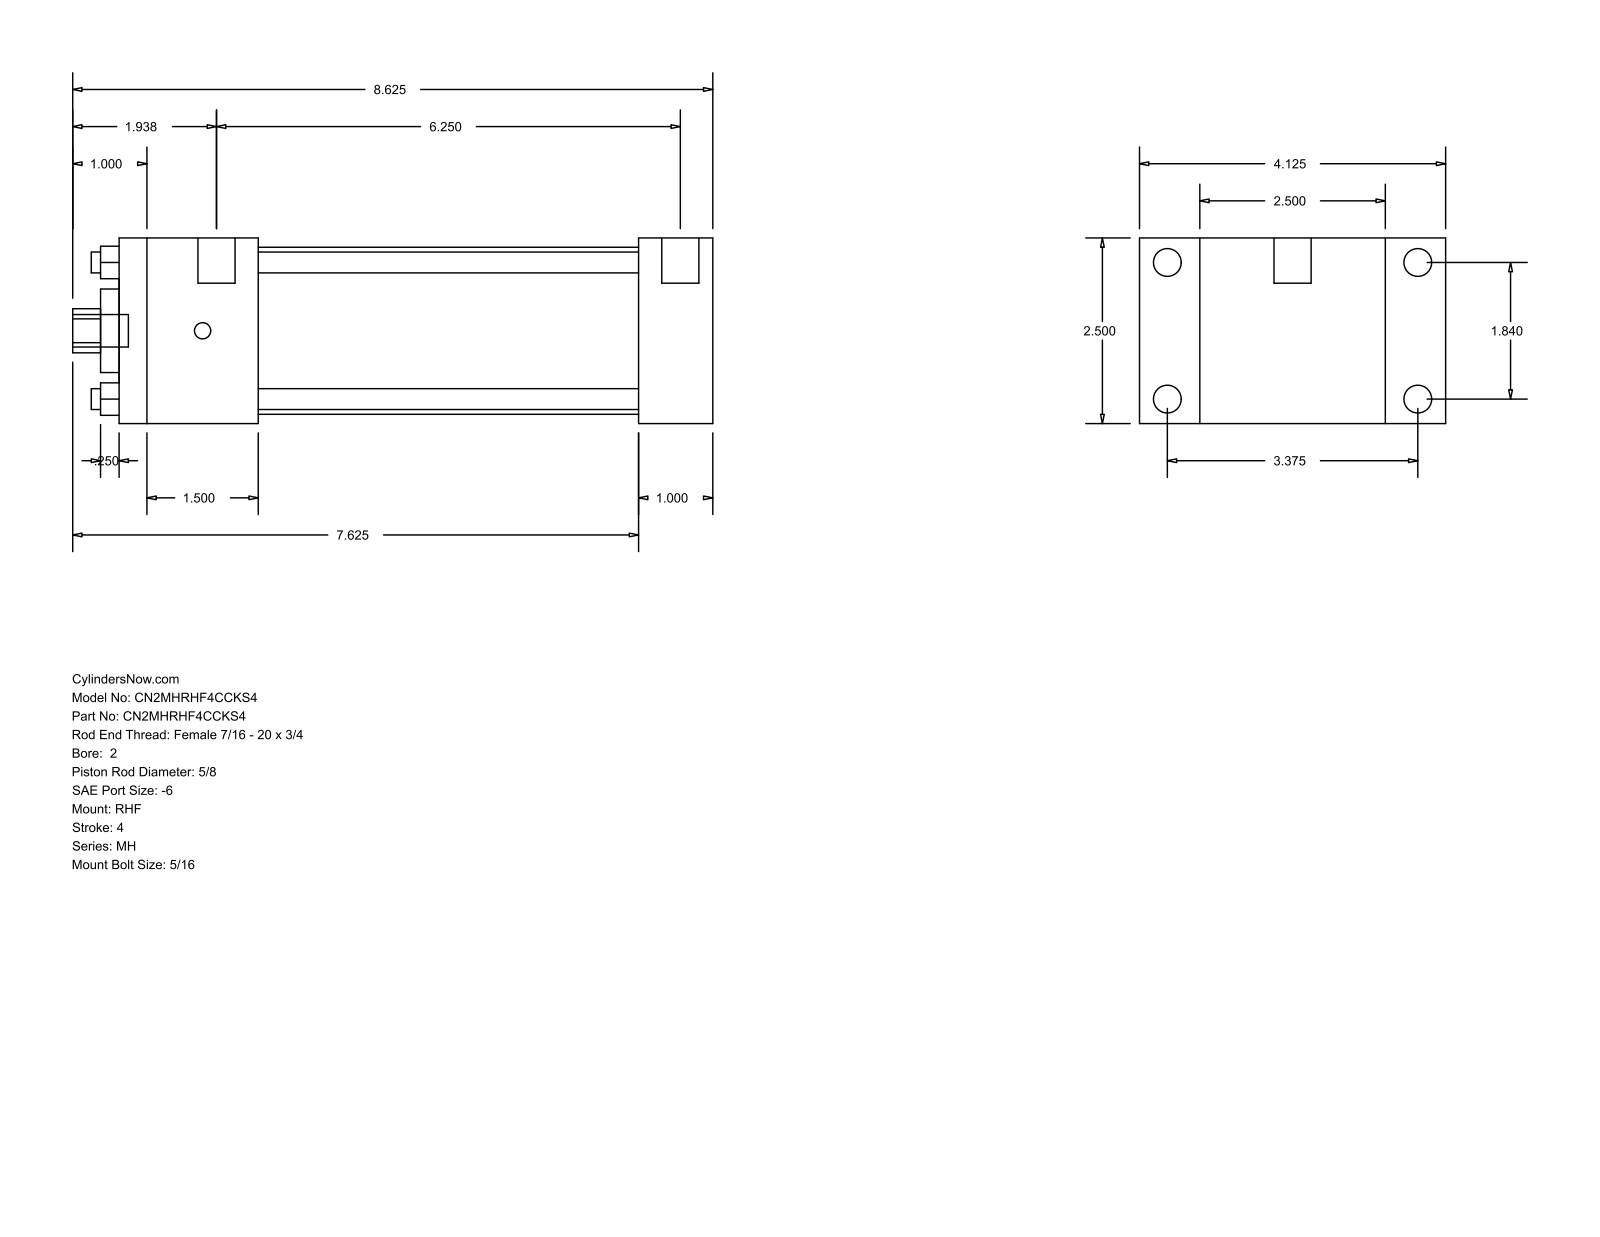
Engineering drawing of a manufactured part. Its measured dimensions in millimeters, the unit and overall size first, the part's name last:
Units: millimetres
Overall size (bounding box): 219.07 × 104.78 × 63.5
Round holes (diameter × count): ⌀7.14 ×4, ⌀15.88 ×1, ⌀28.57 ×1, ⌀57.15 ×1
Round bosses / shafts (diameter × count): ⌀9.53 ×4, ⌀5.56 ×4, ⌀12.7 ×2, ⌀11.11 ×1
Partial cylindrical surfaces — rounded edges, fillets, slot ends (radius × count): R7.54 ×1
Main face-to-face distances: 63.5, 25.39, 20.64, 84.14, 177.8, 203.19, 104.78, 47.62, 130.18, 155.57
Hole centre spacings: 33.05, 46.74, 66.1
Bodies: 0 solids, 88 faces (60 planar, 28 cylindrical, 0 other)
Part name (STEP PRODUCT): MH_RHF__0200_0.625
STEP written by: GSSL Pune (CONFIG_CONTROL_DESIGN)
